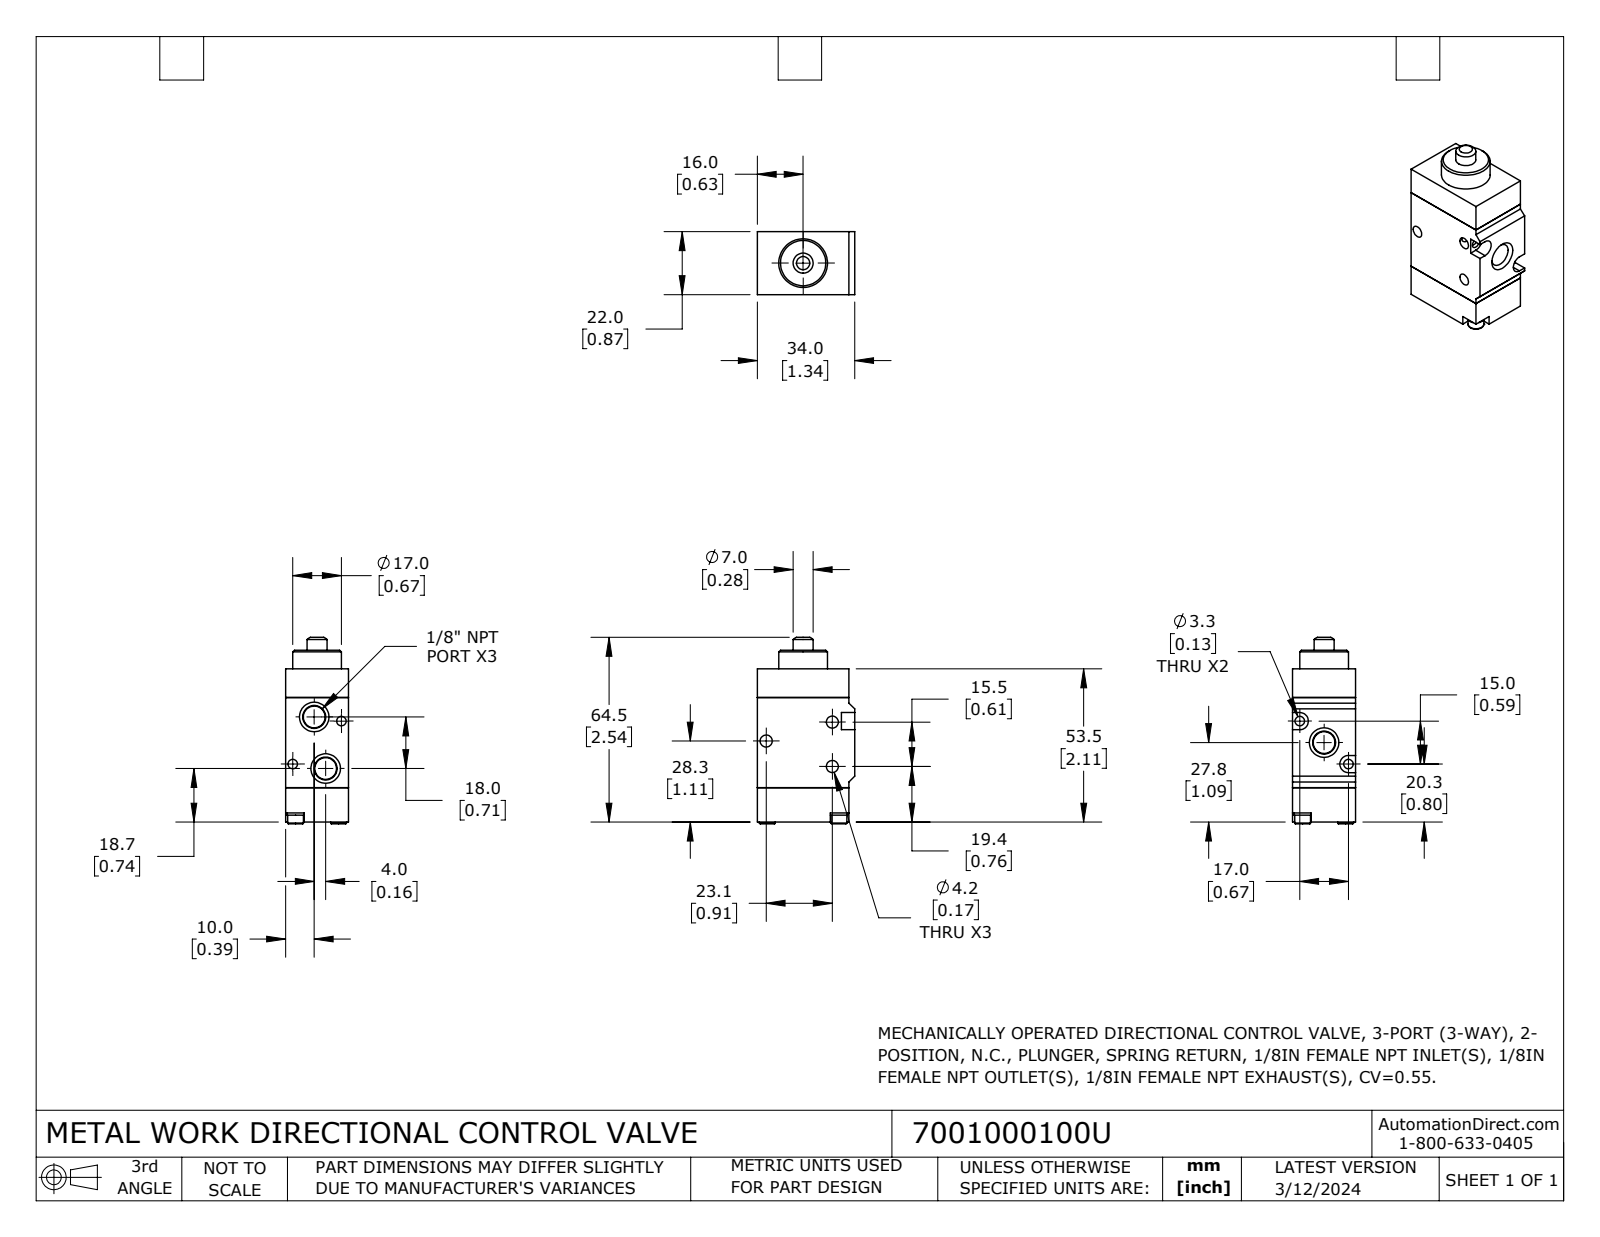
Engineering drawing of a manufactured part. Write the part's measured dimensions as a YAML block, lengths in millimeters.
part_name: "7001000100U"
step_written_by: "SolidWorks 2023 (CONFIG_CONTROL_DESIGN)"
units: millimeters
bodies: {solids: 7, faces: 155, planar: 73, cylindrical: 38, other: 44}
overall_size: [65.1, 34, 22]
volume: 37670
surface_area: 12970
round_holes:
  - {diameter: 4.2, count: 3}
  - {diameter: 3, count: 2}
  - {diameter: 3.3, count: 2}
round_bosses_or_shafts:
  - {diameter: 6, count: 2}
  - {diameter: 5.5, count: 2}
  - {diameter: 17, count: 1}
  - {diameter: 7, count: 1}
partial_cylinders:
  - {radius: 3, count: 2}
face_to_face_distances: [22, 31.5, 12, 43.5, 32, 53.5, 41.5, 10, 2, 34]
hole_center_spacings: [15.5, 22.7, 24, 24.8, 29.2]
